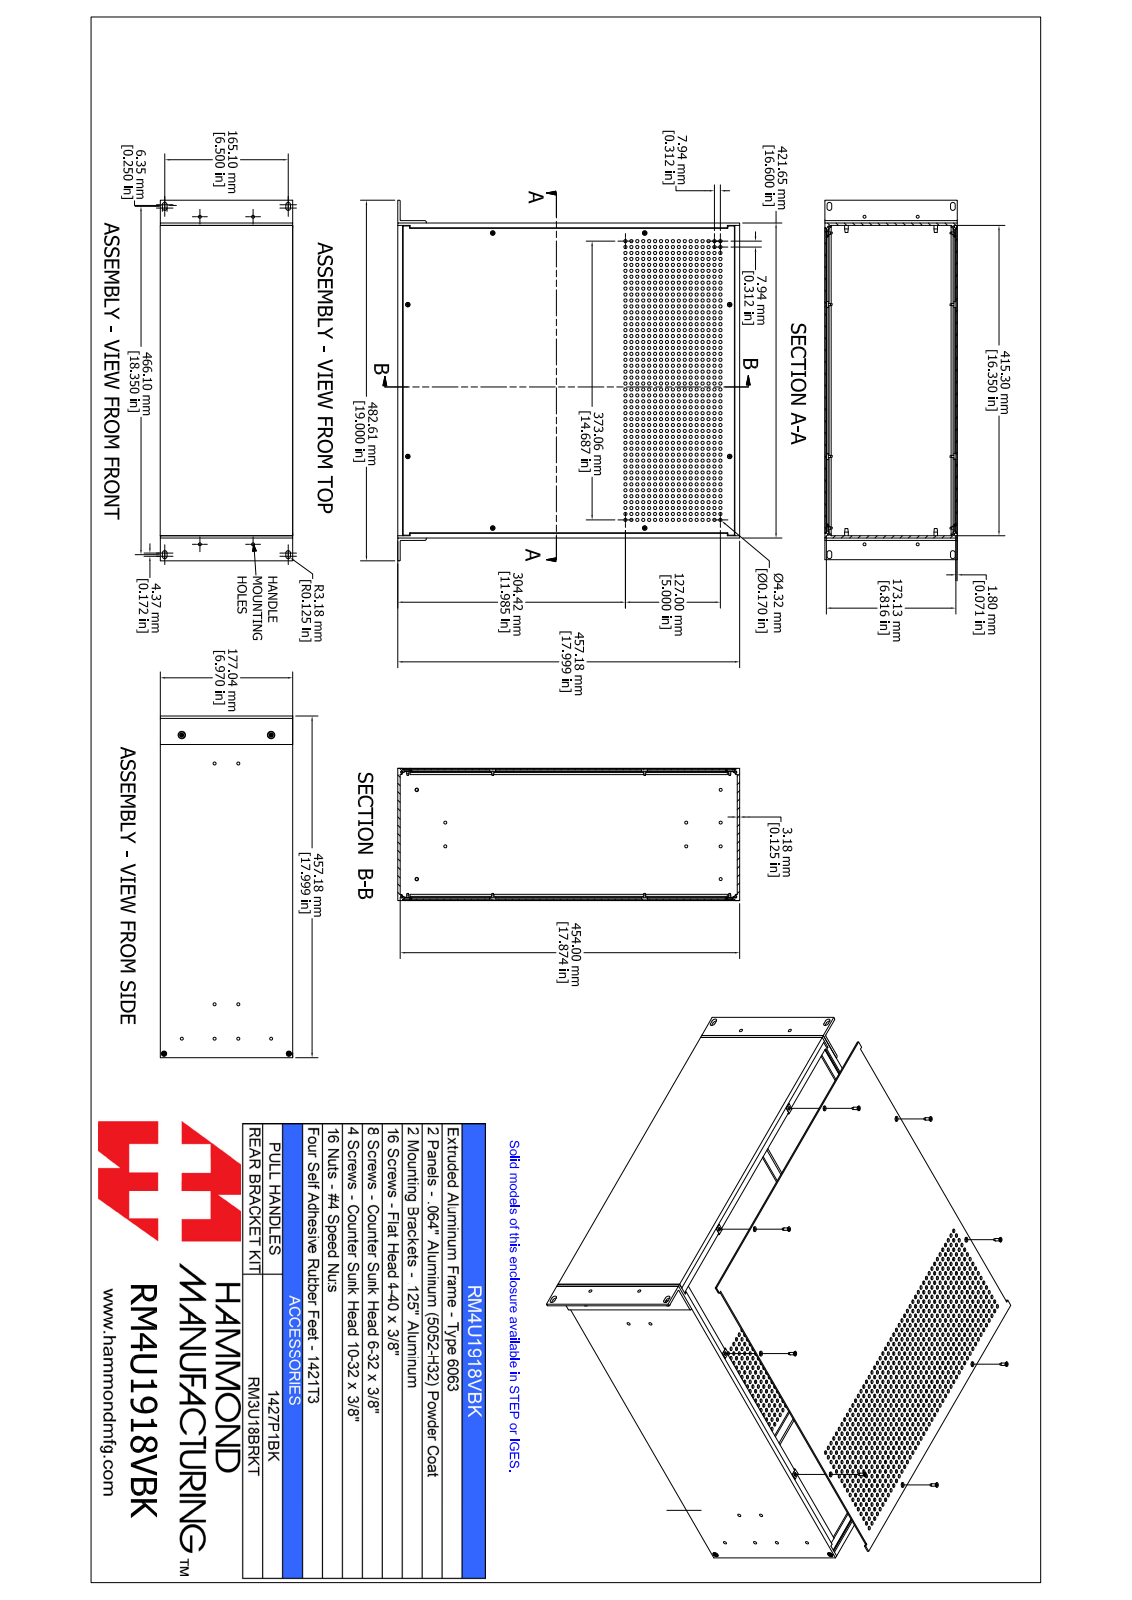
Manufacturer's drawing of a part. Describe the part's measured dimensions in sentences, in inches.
The part is named "RM4U1918VBK". Its 3-D file was written by "SolidWorks 2021 (AUTOMOTIVE_DESIGN)". It is 52 solids with 3016 faces: 636 planar, 1884 cylindrical and 496 other. Overall it measures 19 by 17.999 by 6.971 inches. Its volume is 110.2 cubic inches and its surface area 2 355 square inches. Round holes: 816 of diameter 0.17, 9 of diameter 0.177, 8 of diameter 0.098, 8 of diameter 0.157, 6 of diameter 0.159, 4 of diameter 0.138, 4 of diameter 0.156, 4 of diameter 0.157, 4 of diameter 0.165, 4 of diameter 0.169, 2 of diameter 0.197. Round bosses or shafts: 10 of diameter 0.214, 10 of diameter 0.112, 4 of diameter 0.238, 4 of diameter 0.138, 2 of diameter 0.333, 2 of diameter 0.19. Partial cylindrical surfaces (rounded edges, fillets, slot ends): 22 of radius 0.039, 16 of radius 0.015, 16 of radius 0.038, 16 of radius 0.049, 8 of radius 0.055, 8 of radius 0.125, 8 of radius 0.131, 2 of radius 0.079. The main face-to-face distances are 0.071, 6.887, 0.125, 6.816, 6.958, 16.475, 16.6, 0.125, 16.35, 17.874. The hole center spacings are 1.25, 0.313, 0.937, 8, 1.563, 2.5, 0.625, 2.187.
